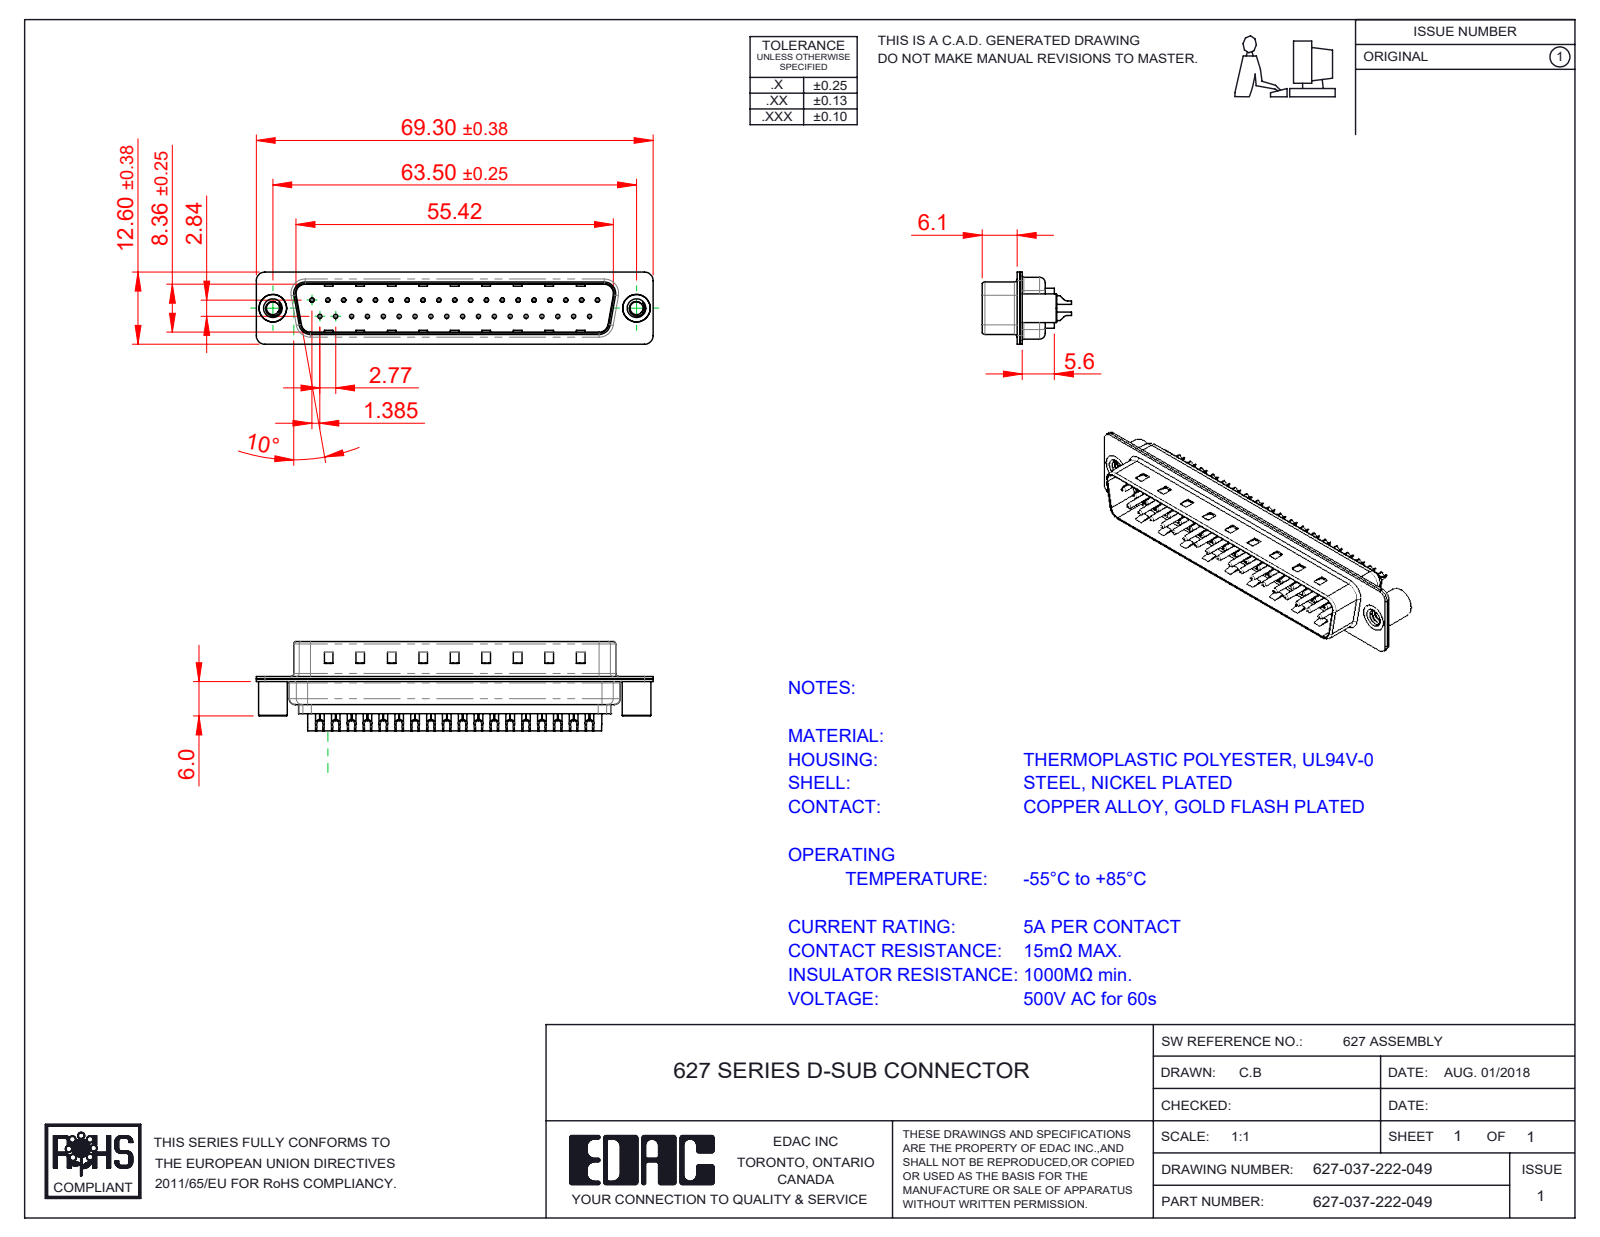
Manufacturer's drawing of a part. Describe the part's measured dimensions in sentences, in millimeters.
The part is named "627-037-222-049; 627 Shell Rear_37 Contacts; 627 Shell Front_37 Contacts; 627 Housing_37 LP (+3 more)". Its 3-D file was written by "SolidWorks 2020 (CONFIG_CONTROL_DESIGN)". It is 42 solids with 2802 faces: 721 planar, 1234 cylindrical and 847 other. Overall it measures 69.3 by 15.35 by 12.6 millimeters. Its volume is 3 810 cubic millimeters and its surface area 10 948 square millimeters. Round holes: 37 of diameter 0.35, 37 of diameter 1.1, 37 of diameter 1.6, 2 of diameter 2.26, 2 of diameter 4, 2 of diameter 4.8. Round bosses or shafts: 37 of diameter 2, 37 of diameter 1.5, 37 of diameter 0.75, 2 of diameter 5, 2 of diameter 4.9. Partial cylindrical surfaces (rounded edges, fillets, slot ends): 16 of radius 1.5, 12 of radius 2, 8 of radius 0.5, 8 of radius 1.6, 6 of radius 1, 4 of radius 0.25, 4 of radius 0.6, 4 of radius 0.65. The main face-to-face distances are 0.4, 0.82, 9.58, 0.45, 8.76, 1.5, 0.9, 1.4, 6.5, 6.05. The hole center spacings are 3.16, 2.77, 5.54, 8.31, 5.04, 10.1, 11.08, 12.78.
